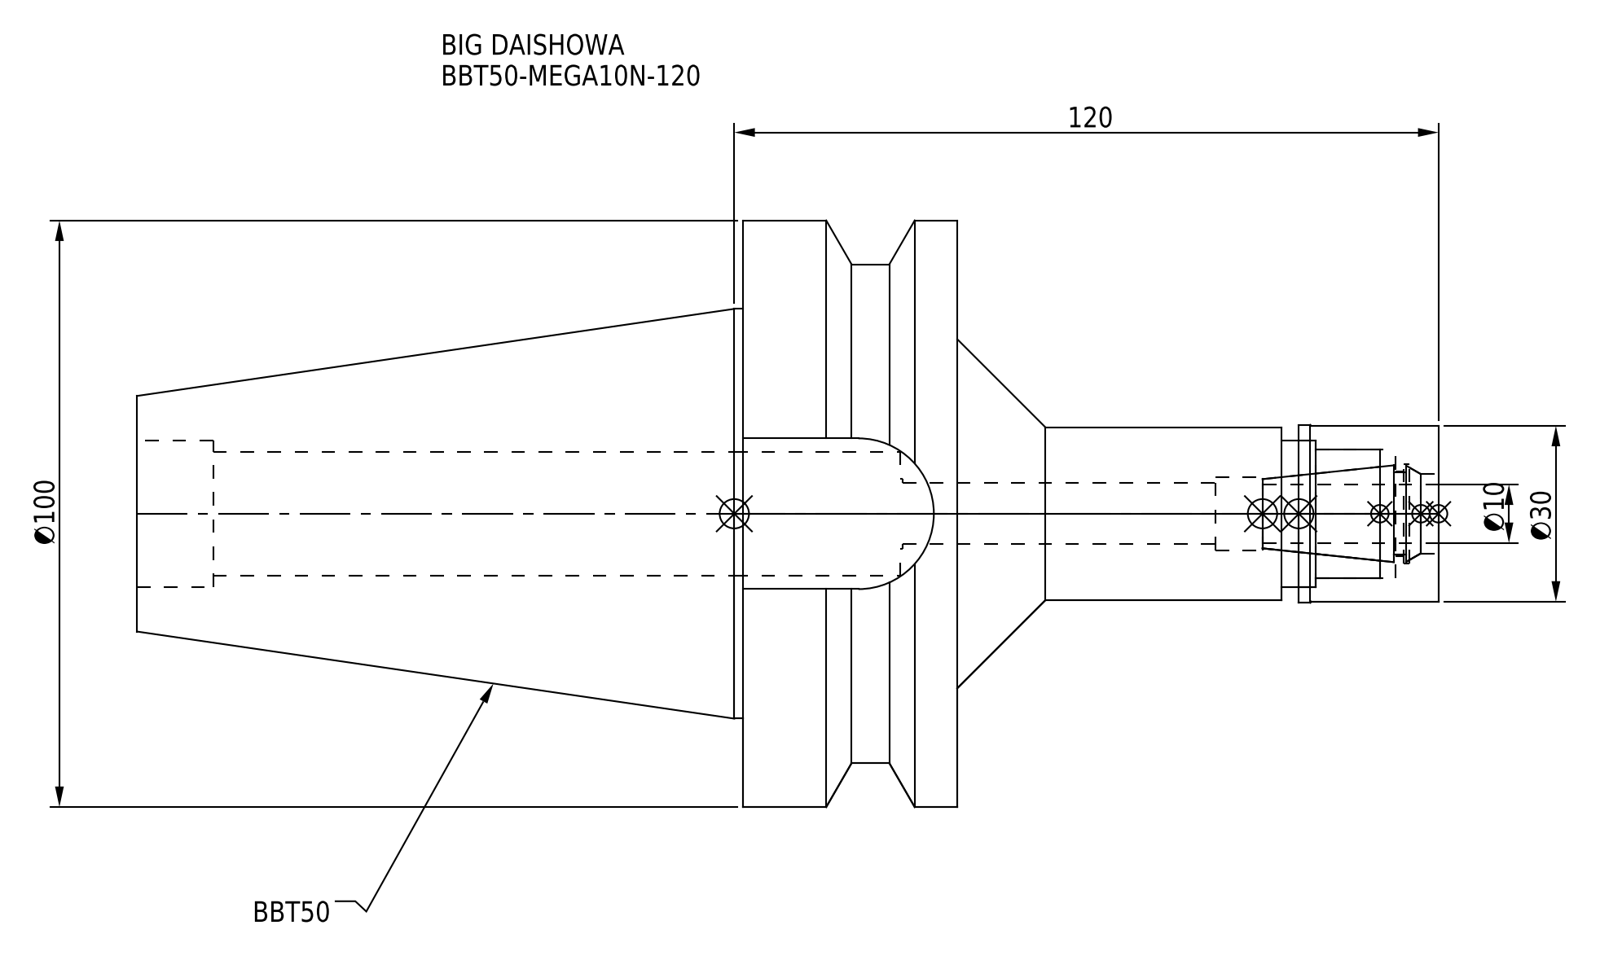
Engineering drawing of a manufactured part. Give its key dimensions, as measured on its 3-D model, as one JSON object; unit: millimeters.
{"part_name": "DXF_TEMP_ASSY_ASM_4_ASM.stp; BBT50MN10120-100_ASM.stp; BBT50-MEGA10N-120-100-FreeParts; BBT50-MEGA10N-120 (+3 more)", "step_written_by": "SolidWorks 2019 (CONFIG_CONTROL_DESIGN)", "units": "millimeters", "bodies": {"solids": 2, "faces": 79, "planar": 23, "cylindrical": 42, "other": 14}, "overall_size": [221.8, 100, 100], "volume_mm3": 510456, "surface_area_mm2": 67674, "round_holes": [[10.4, 1], [12, 1], [12.5, 1], [13.5, 1], [14.5, 1], [17, 1], [21.2, 1], [22, 1], [25, 1]], "round_bosses_or_shafts": [[100, 1], [85, 1], [69.85, 1], [30.3, 1], [30, 1], [29.5, 1]], "partial_cylinders_radius": [[12.85, 1]], "face_to_face_distances": [36.5, 139.8, 103.3, 70.8, 82, 118.5, 221.8, 25.7, 91.8, 9.8]}
